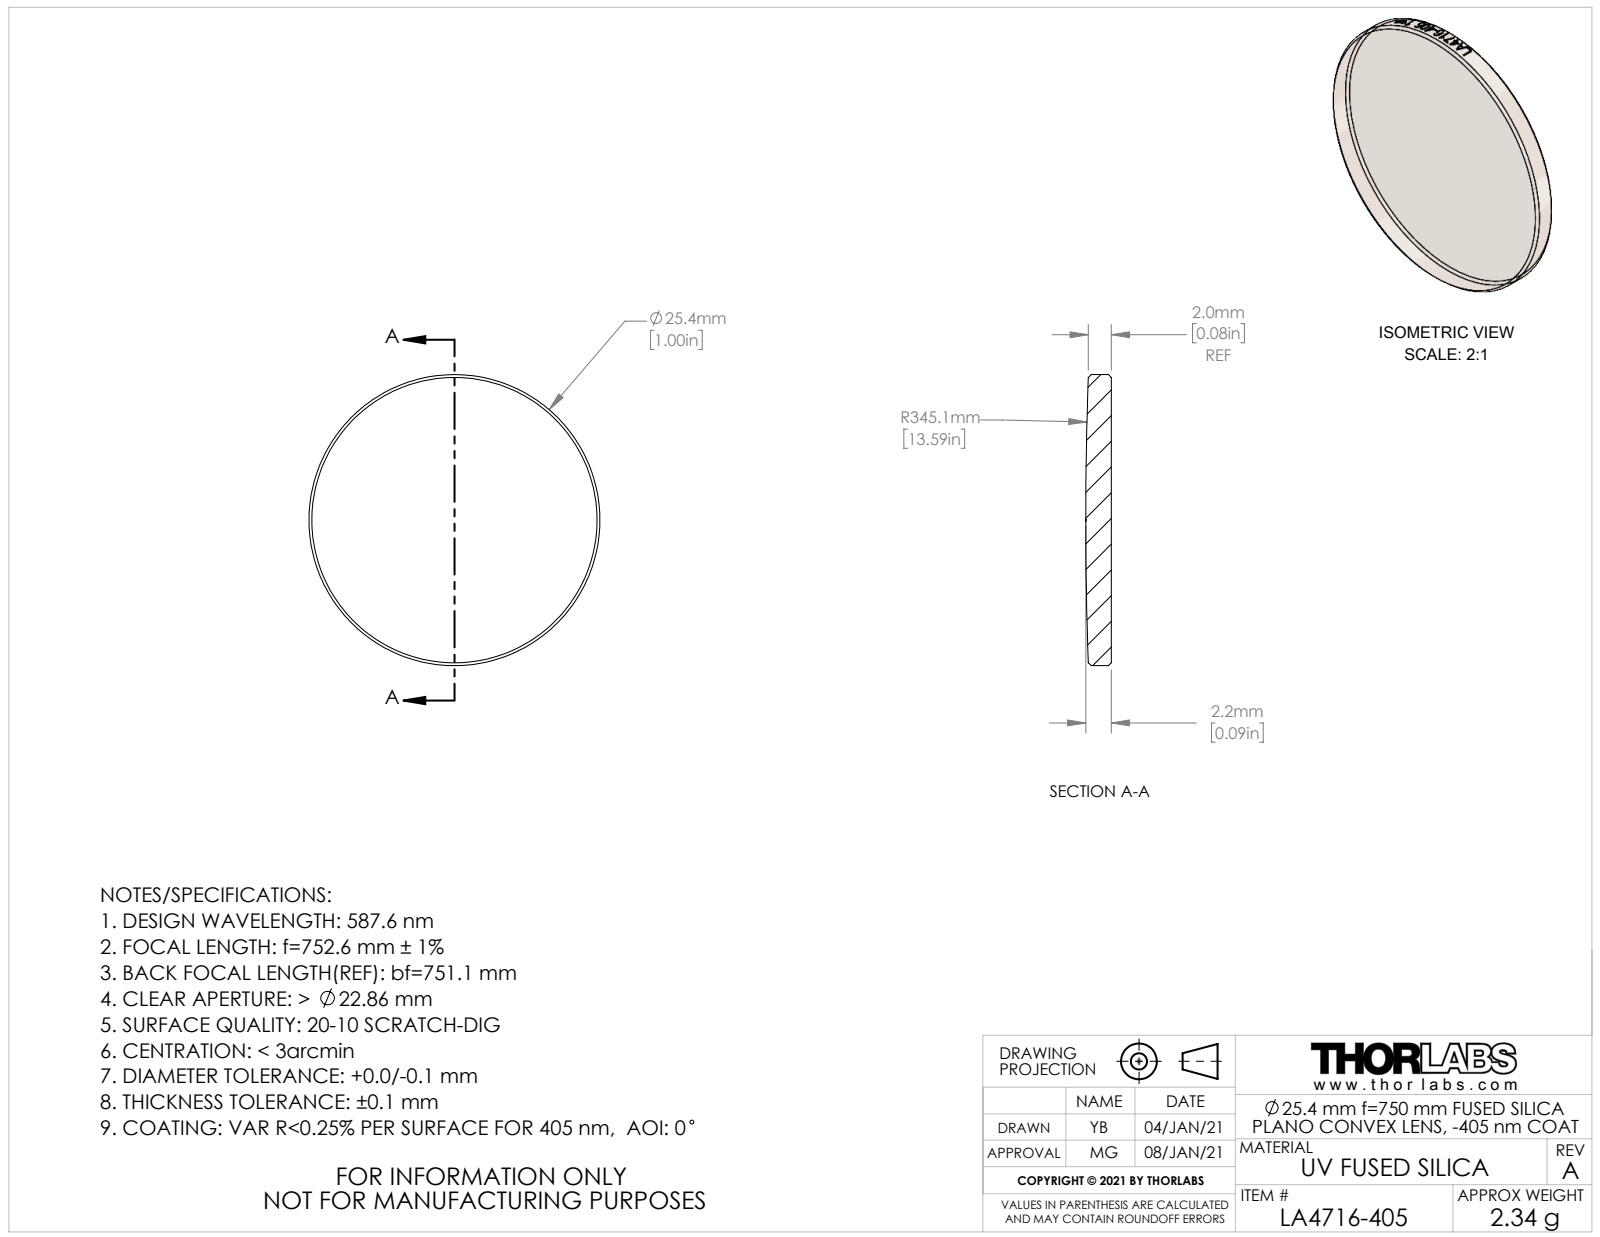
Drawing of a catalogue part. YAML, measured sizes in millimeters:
part_name: "CTN016829-E0W; CTN016849"
step_written_by: "SolidWorks 2018 (AUTOMOTIVE_DESIGN)"
units: millimeters
bodies: {solids: 1, faces: 28, planar: 1, cylindrical: 21, other: 6}
overall_size: [25.4, 25.4, 2.2]
volume: 1100
surface_area: 1150
round_bosses_or_shafts:
  - {diameter: 25.4, count: 1}
